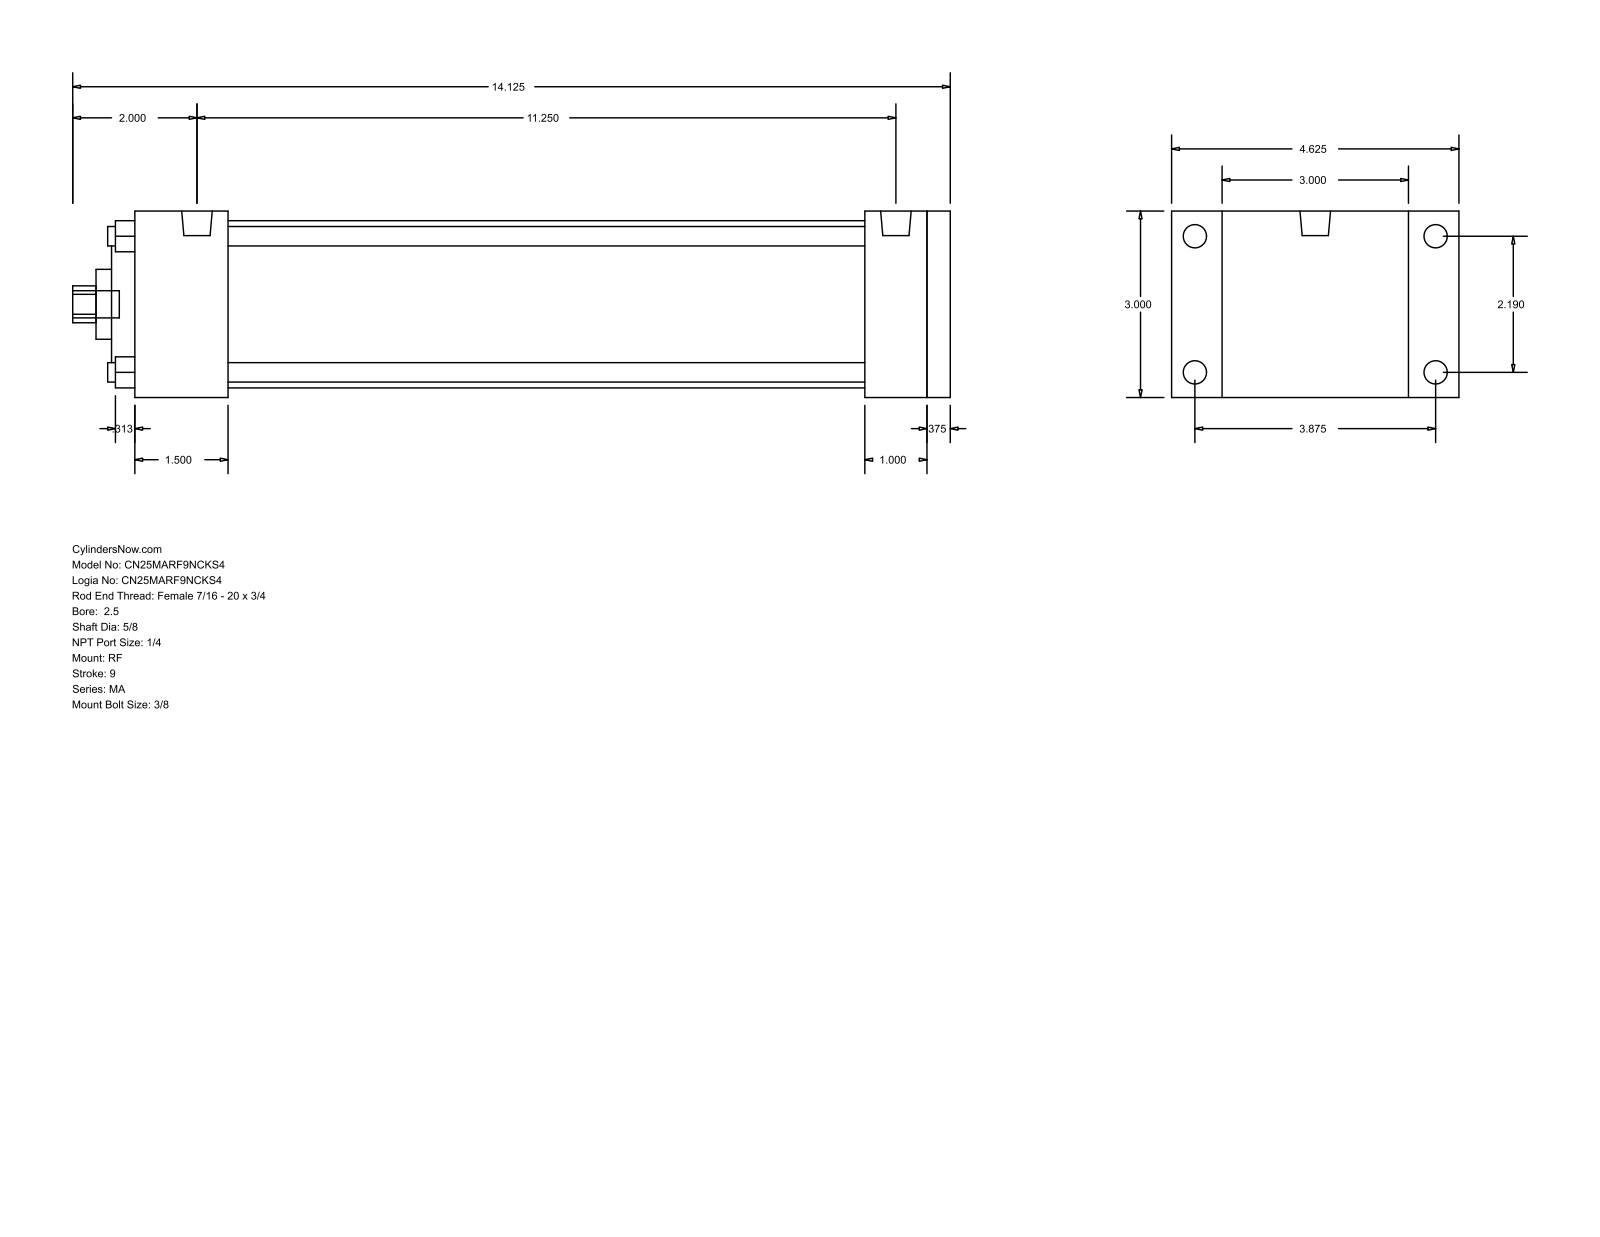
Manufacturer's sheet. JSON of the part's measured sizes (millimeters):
{"part_name": "MA_RF__0250_0.625", "step_written_by": "GSSL Pune (CONFIG_CONTROL_DESIGN)", "units": "millimeters", "bodies": {"solids": 0, "faces": 94, "planar": 65, "cylindrical": 29, "other": 0}, "overall_size": [358.77, 117.47, 76.2], "round_holes": [[7.94, 4], [15.88, 1], [28.57, 1], [50.8, 1], [68.33, 1]], "round_bosses_or_shafts": [[9.53, 4], [7.94, 4], [12.49, 2], [11.11, 1]], "partial_cylinders_radius": [[7.54, 1]], "face_to_face_distances": [76.2, 333.37, 9.52, 323.85, 25.4, 38.1, 298.45, 260.35, 285.75, 295.27], "hole_center_spacings": [39.33, 55.62, 78.66]}
